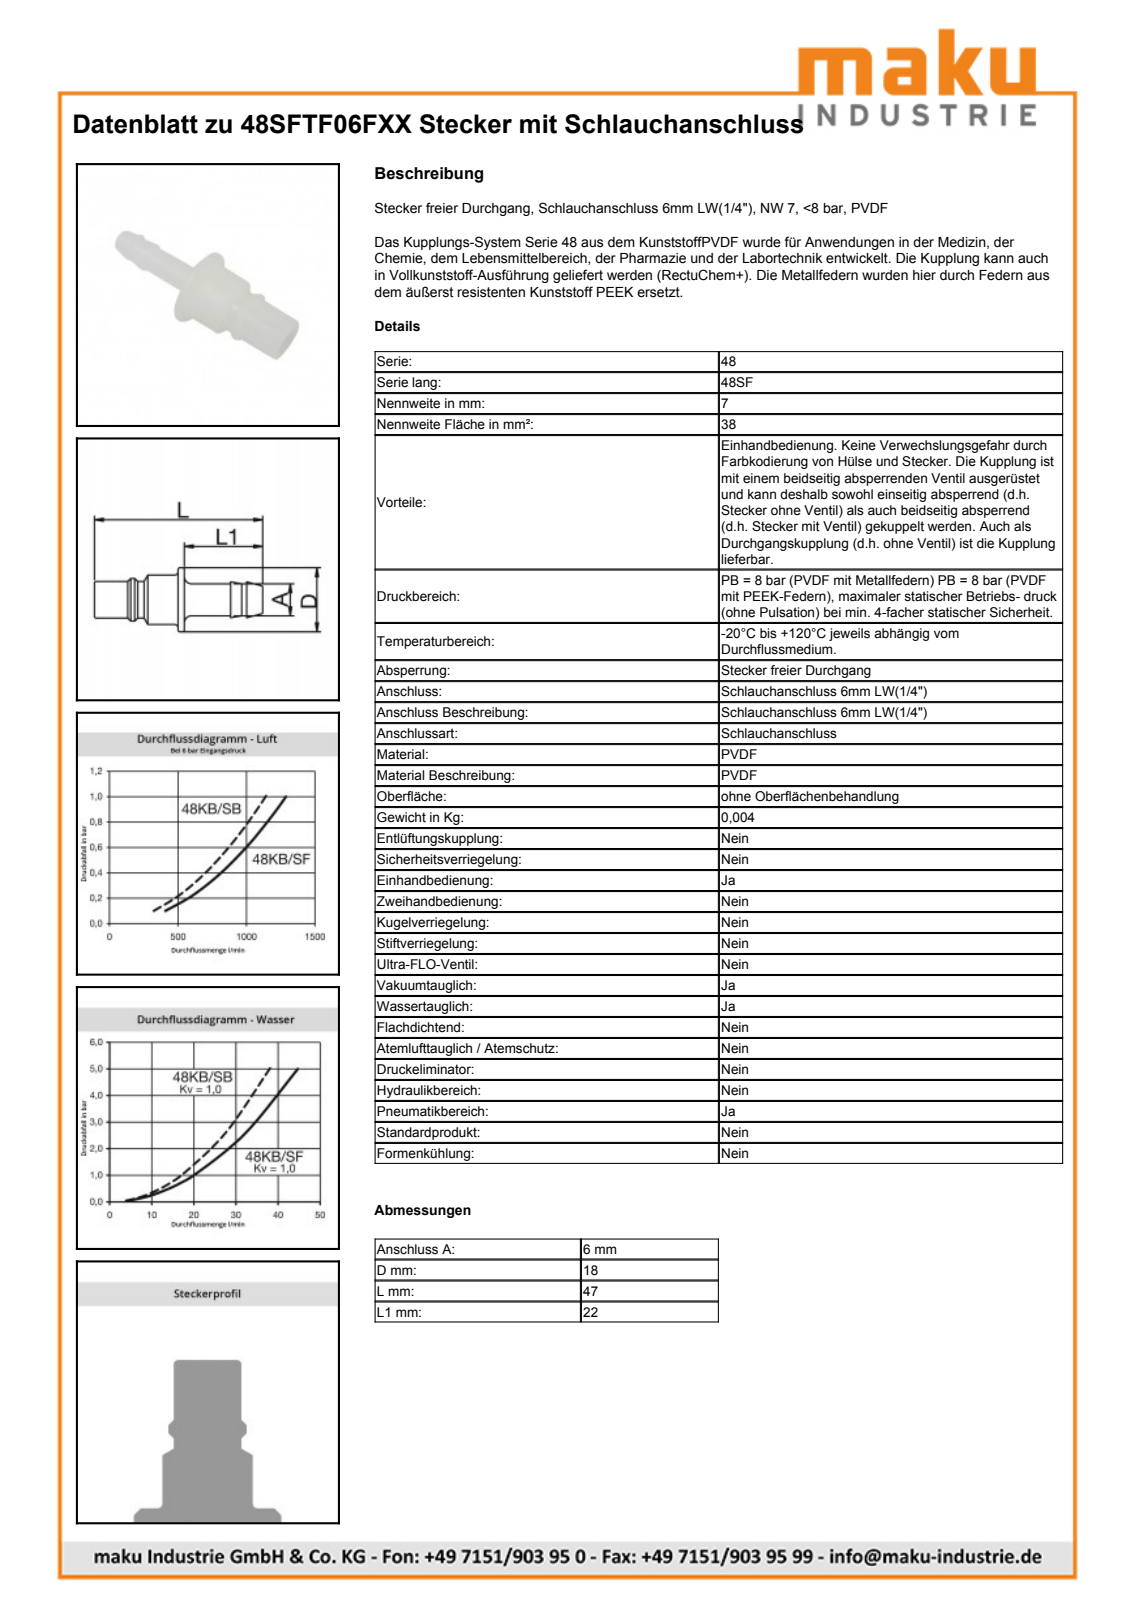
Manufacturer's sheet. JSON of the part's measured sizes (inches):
{"part_name": "48SFTF06FXX", "step_written_by": "Autodesk Inventor 2016 (AUTOMOTIVE_DESIGN)", "units": "inches", "bodies": {"solids": 1, "faces": 28, "planar": 6, "cylindrical": 9, "other": 13}, "overall_size": [1.86, 0.709, 0.709], "volume_in3": 0.159, "surface_area_in2": 4.011, "round_holes": [[0.142, 1], [0.276, 1]], "round_bosses_or_shafts": [[0.709, 1], [0.547, 1], [0.472, 1], [0.409, 1], [0.406, 1], [0.236, 1]], "face_to_face_distances": [0.069, 0.925, 0.994, 0.177, 1.506, 1.683, 0.581, 0.758, 0.512, 0.689]}
